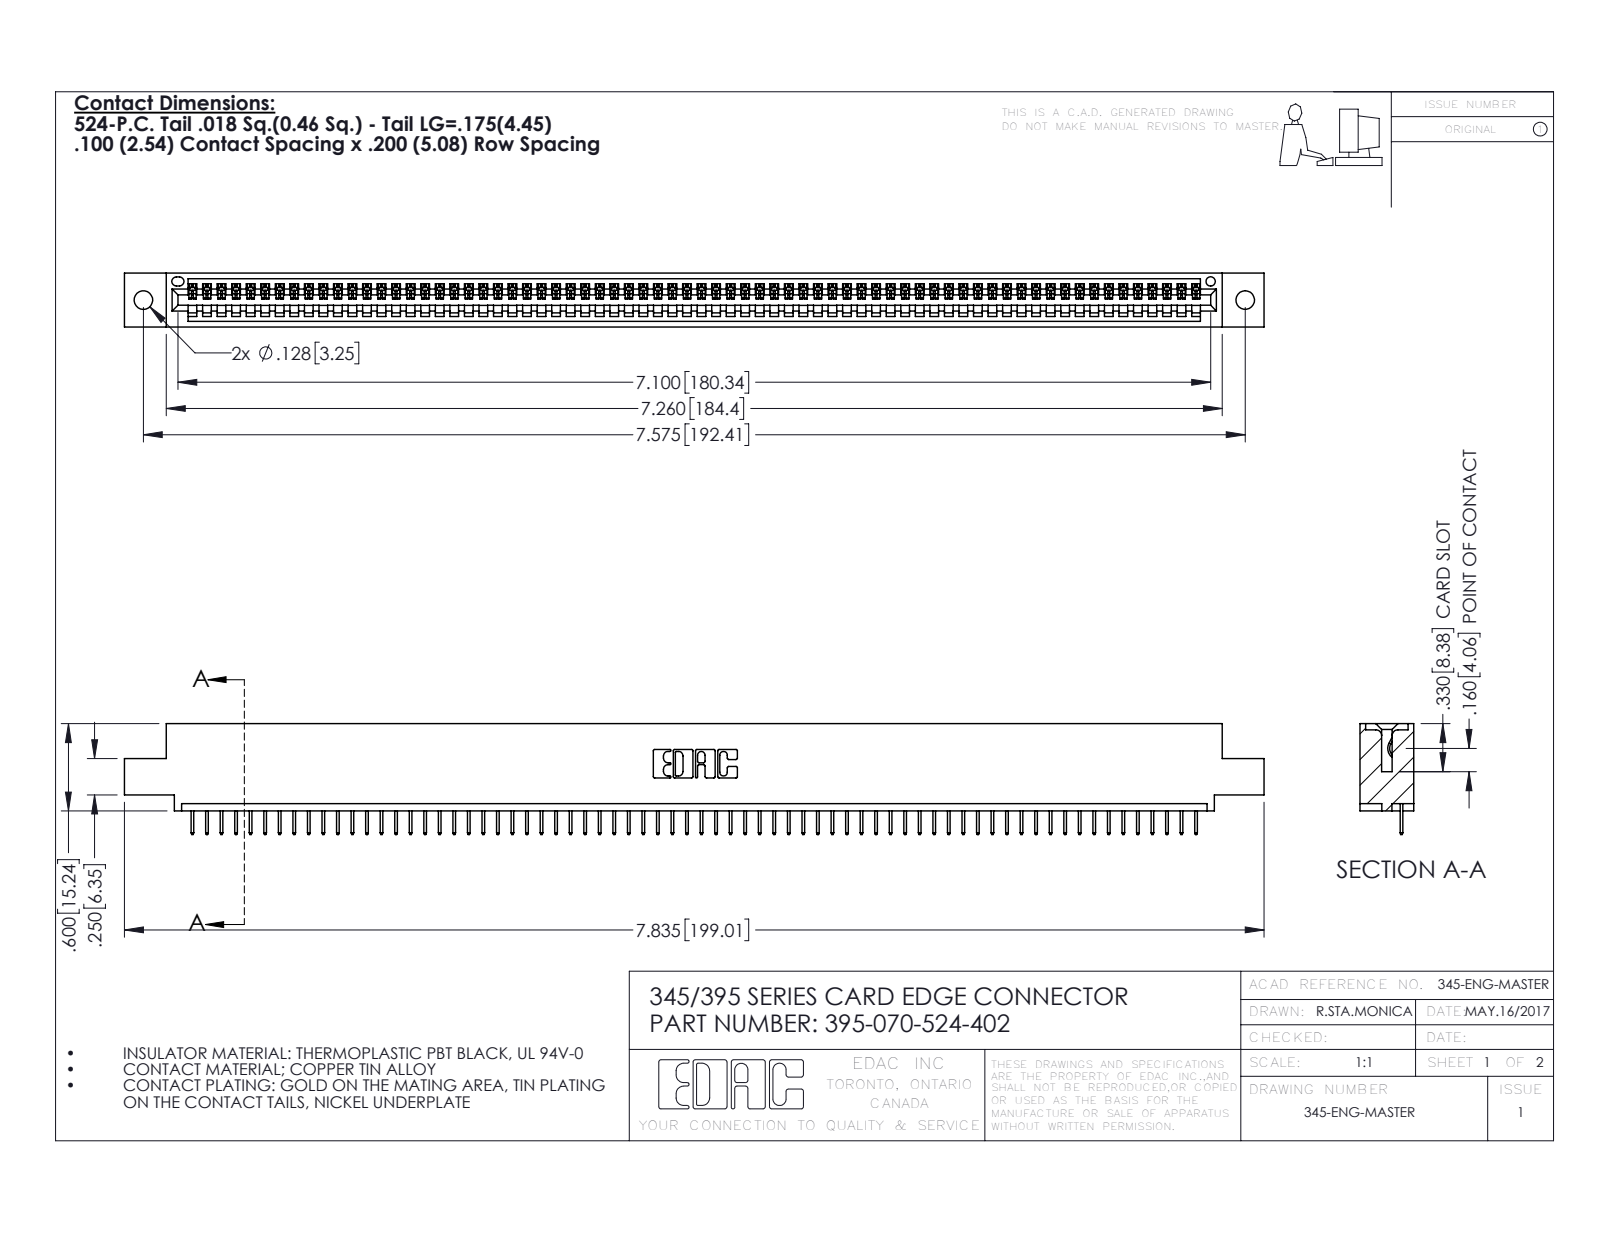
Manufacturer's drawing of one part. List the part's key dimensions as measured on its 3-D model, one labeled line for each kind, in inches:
Part name (STEP PRODUCT): 345 Part_0.110 Offset - 0.128 Dia; 345-292-001_345-293-124; 395-070-524-402
STEP written by: SolidWorks 2016 (CONFIG_CONTROL_DESIGN)
Units: inches
Bodies: 71 solids, 4470 faces (3304 planar, 1166 cylindrical, 0 other)
Overall size (bounding box): 7.835 × 0.762 × 0.37
Volume: 1.144 in³ · Surface area: 37.54 in²
Round holes (diameter × count): ⌀0.128 ×2, ⌀0.064 ×1
Partial cylindrical surfaces — rounded edges, fillets, slot ends (radius × count): R0.006 ×140, R0.01 ×22, R0.007 ×6, R0.031 ×6, R0.026 ×3, R0.031 ×2, R0.04 ×2, R0.014 ×1
Main face-to-face distances: 0.072, 0.298, 0.37, 0.2, 0.098, 0.272, 0.025, 0.225, 0.072, 0.149
Hole centre spacings: 0.27, 7.339, 7.575
